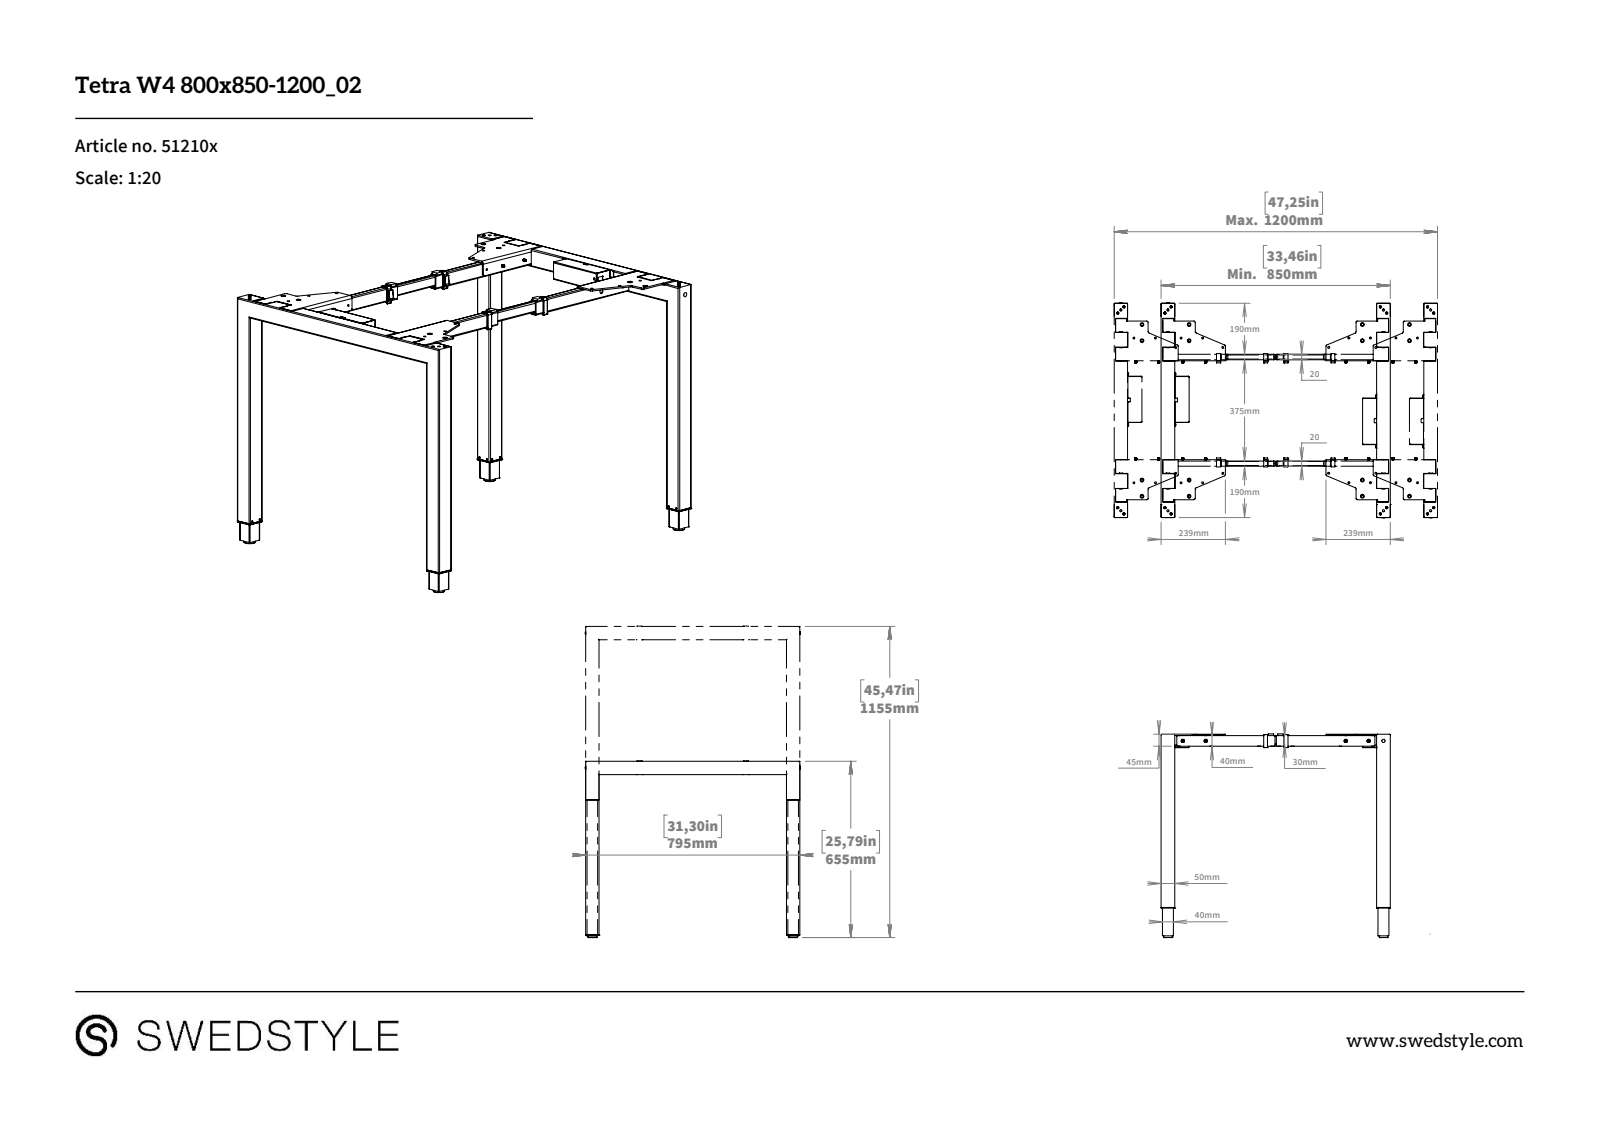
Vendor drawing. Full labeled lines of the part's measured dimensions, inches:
Part name (STEP PRODUCT): 51210x_Tetra W4 800x850-1200_2020
STEP written by: SolidWorks 2019 (CONFIG_CONTROL_DESIGN)
Units: inches
Bodies: 0 solids, 1035 faces (441 planar, 394 cylindrical, 200 other)
Overall size (bounding box): 39.181 × 31.457 × 27.787
Round holes (diameter × count): ⌀0.276 ×12, ⌀0.197 ×10, ⌀0.268 ×8, ⌀0.354 ×8, ⌀0.157 ×4, ⌀0.236 ×4, ⌀0.315 ×4, ⌀0.472 ×4, ⌀0.165 ×2
Round bosses / shafts (diameter × count): ⌀0.236 ×4
Partial cylindrical surfaces — rounded edges, fillets, slot ends (radius × count): R0.02 ×38, R0.118 ×36, R0.079 ×16, R0.098 ×16, R0.197 ×14, R0.059 ×12, R0.03 ×8, R0.091 ×8
Main face-to-face distances: 1.969, 37.205, 0.079, 0.157, 15.551, 29.331, 0.709, 35.236, 39.173, 1.811
Hole centre spacings: 2.362, 1.245, 2.007, 2.296, 2.784, 3.15, 3.258, 3.751
